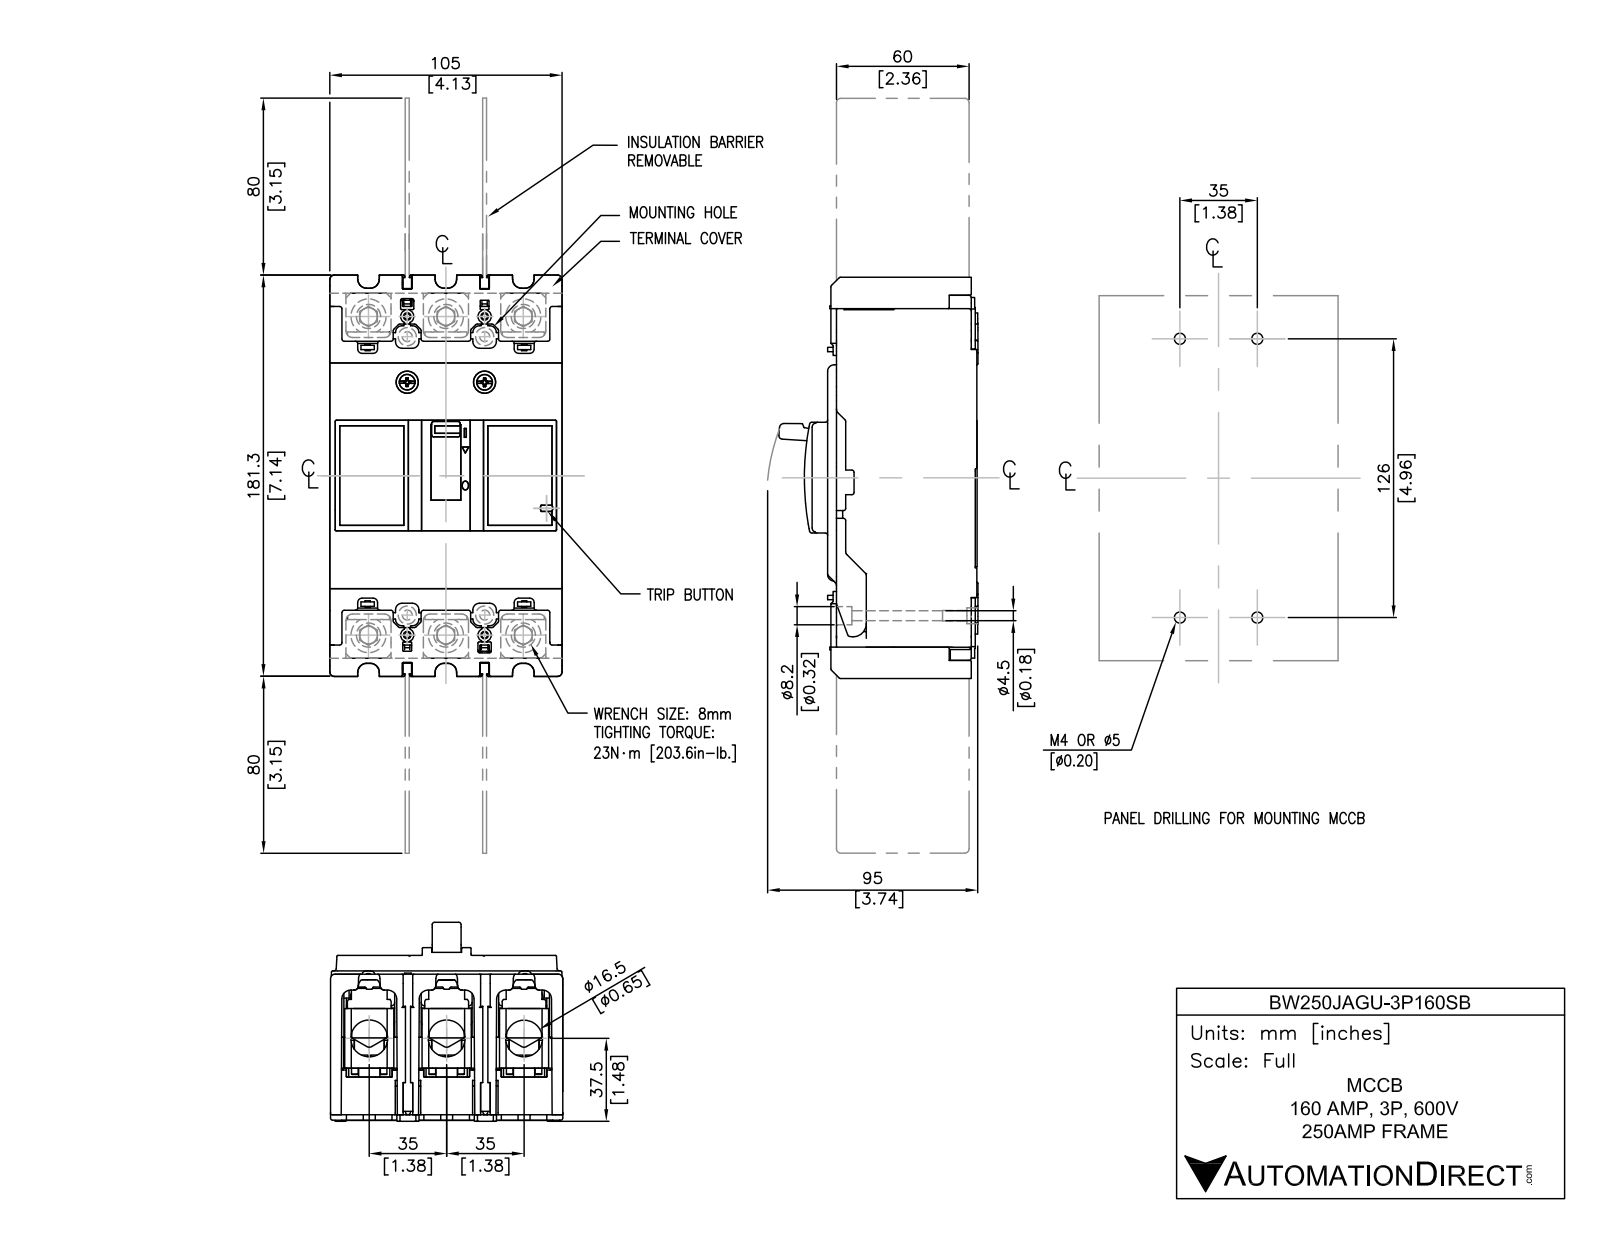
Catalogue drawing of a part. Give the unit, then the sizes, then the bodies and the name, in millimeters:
Units: millimetres
Overall size (bounding box): 189 × 105 × 91
Round holes (diameter × count): ⌀8 ×6, ⌀4.5 ×4, ⌀8.2 ×4
Round bosses / shafts (diameter × count): ⌀13 ×6
Partial cylindrical surfaces — rounded edges, fillets, slot ends (radius × count): R1 ×36, R3 ×16, R2 ×8, R12.5 ×3
Main face-to-face distances: 2.5, 63.5, 105, 35, 20, 66, 31.5, 8.5, 4, 1.5
Hole centre spacings: 19.7, 136.1, 35, 53.3, 144.9, 148.2, 144, 70
Volume: 1 107 000 mm³ · Surface area: 144 500 mm²
Bodies: 10 solids, 471 faces (338 planar, 121 cylindrical, 12 other)
Part name (STEP PRODUCT): BW250JAGU-3P160SB
STEP written by: SolidWorks 2018 (AUTOMOTIVE_DESIGN)
